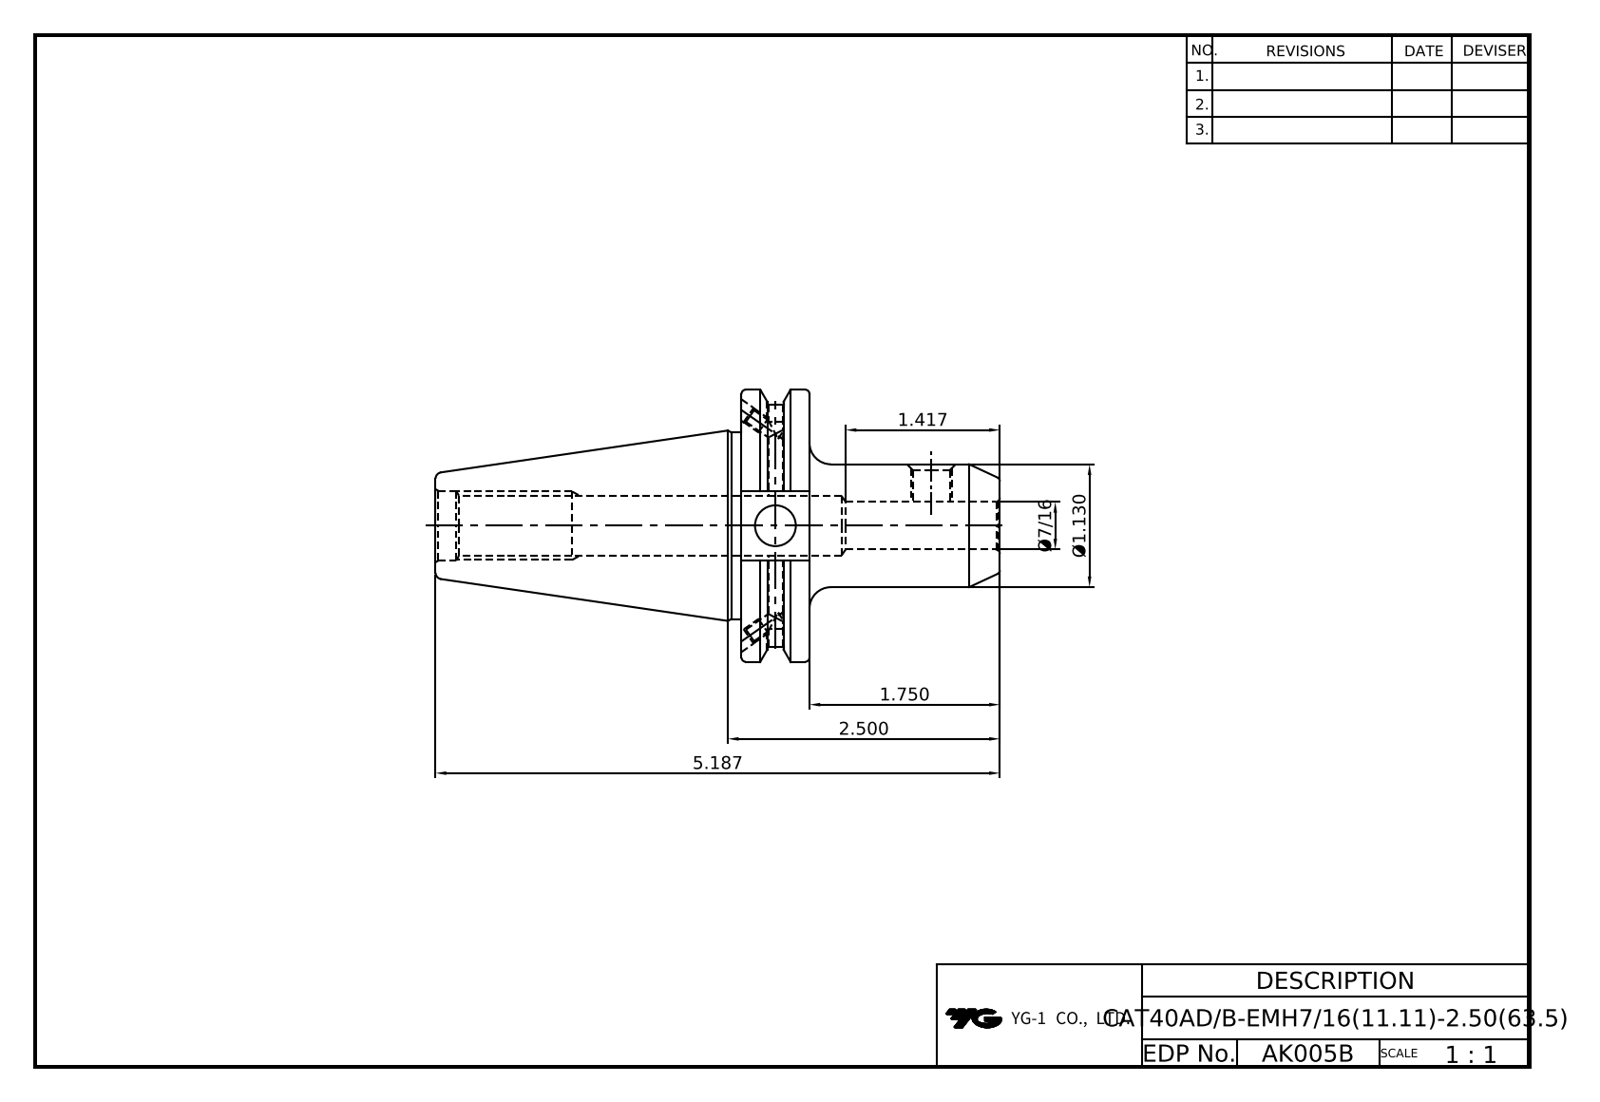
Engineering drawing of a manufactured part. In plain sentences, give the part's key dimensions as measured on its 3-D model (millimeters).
The part is named "LO-CAT40ADB-EMH11.1125-63.5". Its 3-D file was written by "Autodesk Inventor 2025 (AUTOMOTIVE_DESIGN)". It is 1 solid with 85 faces: 35 planar, 27 cylindrical and 23 other. Overall it measures 131.75 by 63.5 by 61.09 millimeters. Its volume is 122 997 cubic millimeters and its surface area 26 204 square millimeters. Round holes: 4 of diameter 3.24, 2 of diameter 4, 2 of diameter 4.2, 1 of diameter 8.38, 1 of diameter 9.53, 1 of diameter 11.11, 1 of diameter 13.39, 1 of diameter 16.3. Round bosses or shafts: 1 of diameter 63.5, 1 of diameter 43.6, 1 of diameter 28.7. Partial cylindrical surfaces (rounded edges, fillets, slot ends): 1 of radius 28.15. The main face-to-face distances are 15.88, 60.33, 44.45, 47.6, 16.38, 71.42, 87.3, 131.75, 77.47, 6.05.
